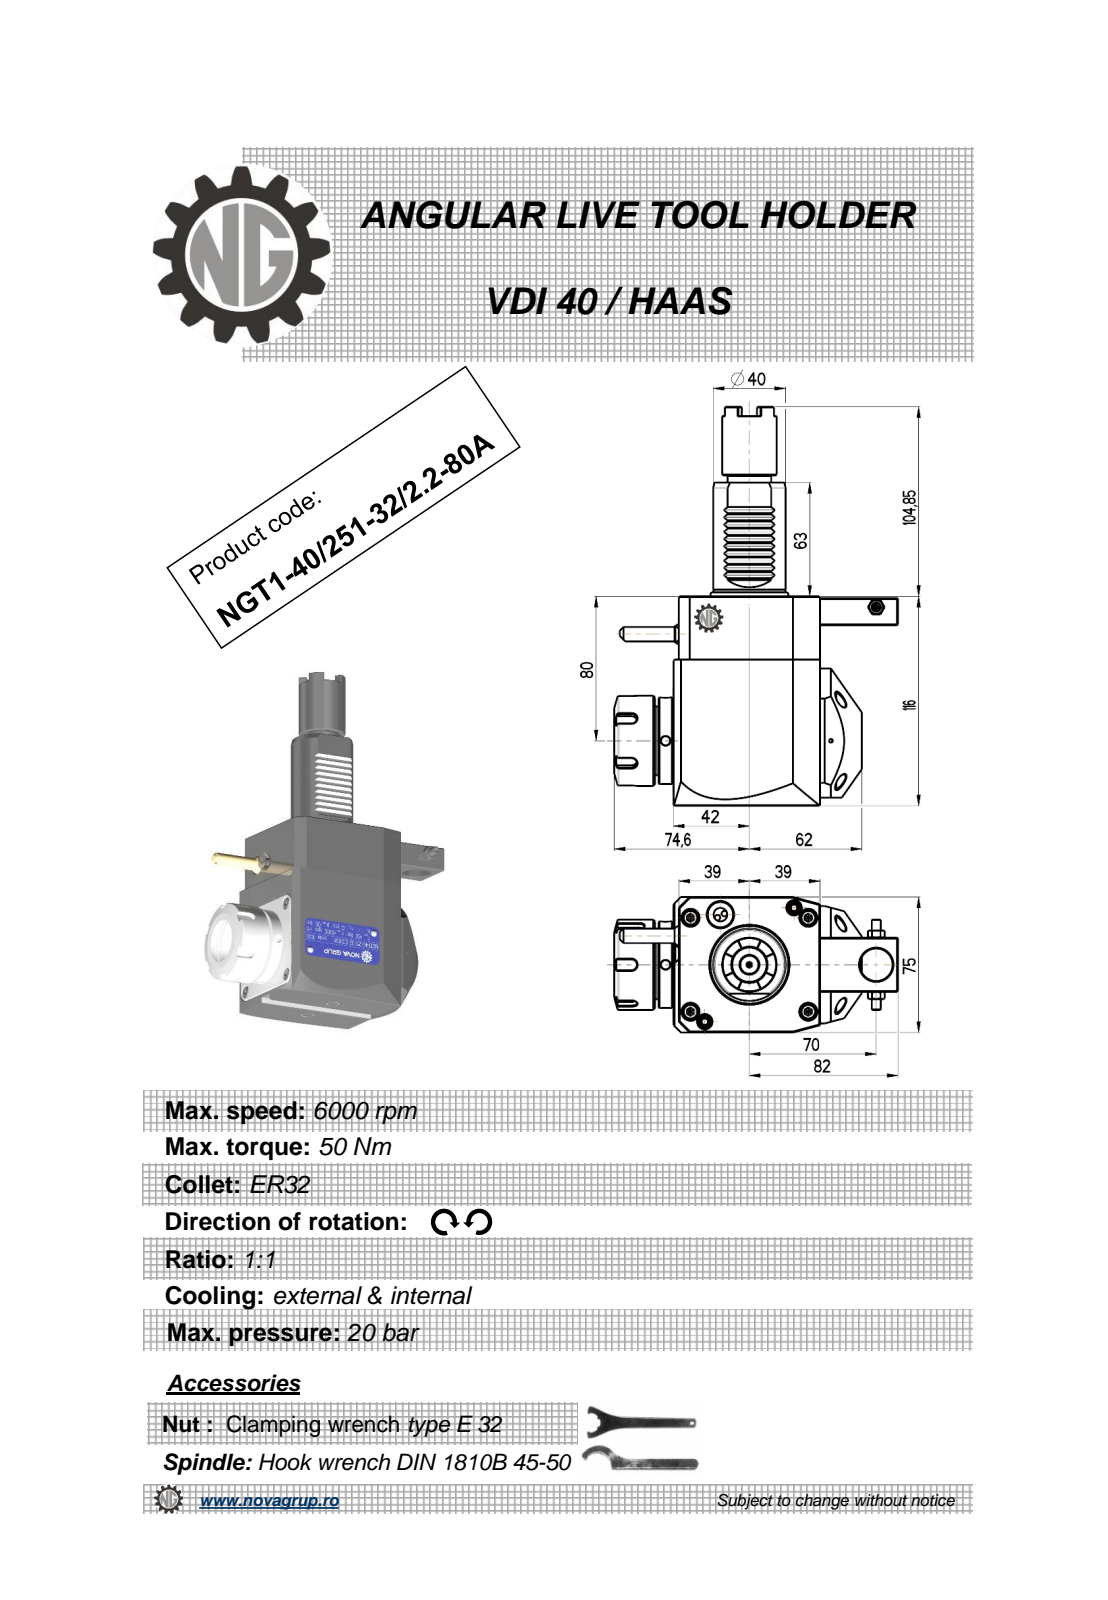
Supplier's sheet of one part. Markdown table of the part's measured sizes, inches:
| quantity | value |
| --- | --- |
| part name | NGT1_40_251_32_2_2_80A |
| STEP written by | PRO/ENGINEER BY PARAMETRIC TECHNOLOGY CORPORATION, 2010280 (CONFIG_CONTROL_DESIGN) |
| units | inches |
| bodies | 1 solid, 449 faces (222 planar, 94 cylindrical, 133 other) |
| overall size | 8.695 × 6.165 × 2.953 |
| volume | 56.28 in³ |
| surface area | 118.4 in² |
| round holes (diameter × count) | 0.197 × 3, 0.118 × 1, 0.165 × 1, 0.374 × 1, 0.709 × 1, 1.063 × 1 |
| round bosses / shafts (diameter × count) | 1.969 × 1, 1.89 × 1, 1.614 × 1, 1.575 × 1, 1.181 × 1, 0.945 × 1, 0.394 × 1, 0.353 × 1 |
| partial cylindrical surfaces (radius × count) | 0.01 × 12, 0.012 × 10, 0.008 × 6, 0.118 × 5, 0.02 × 1, 0.384 × 1, 1.575 × 1 |
| main face-to-face distances | 2.953, 4.567, 3.189, 0.118, 3.071, 0.11, 3.181, 0.039, 0.886, 4.409 |
| hole center spacings | 0.824, 2.407, 2.854, 4.577, 5.425 |
